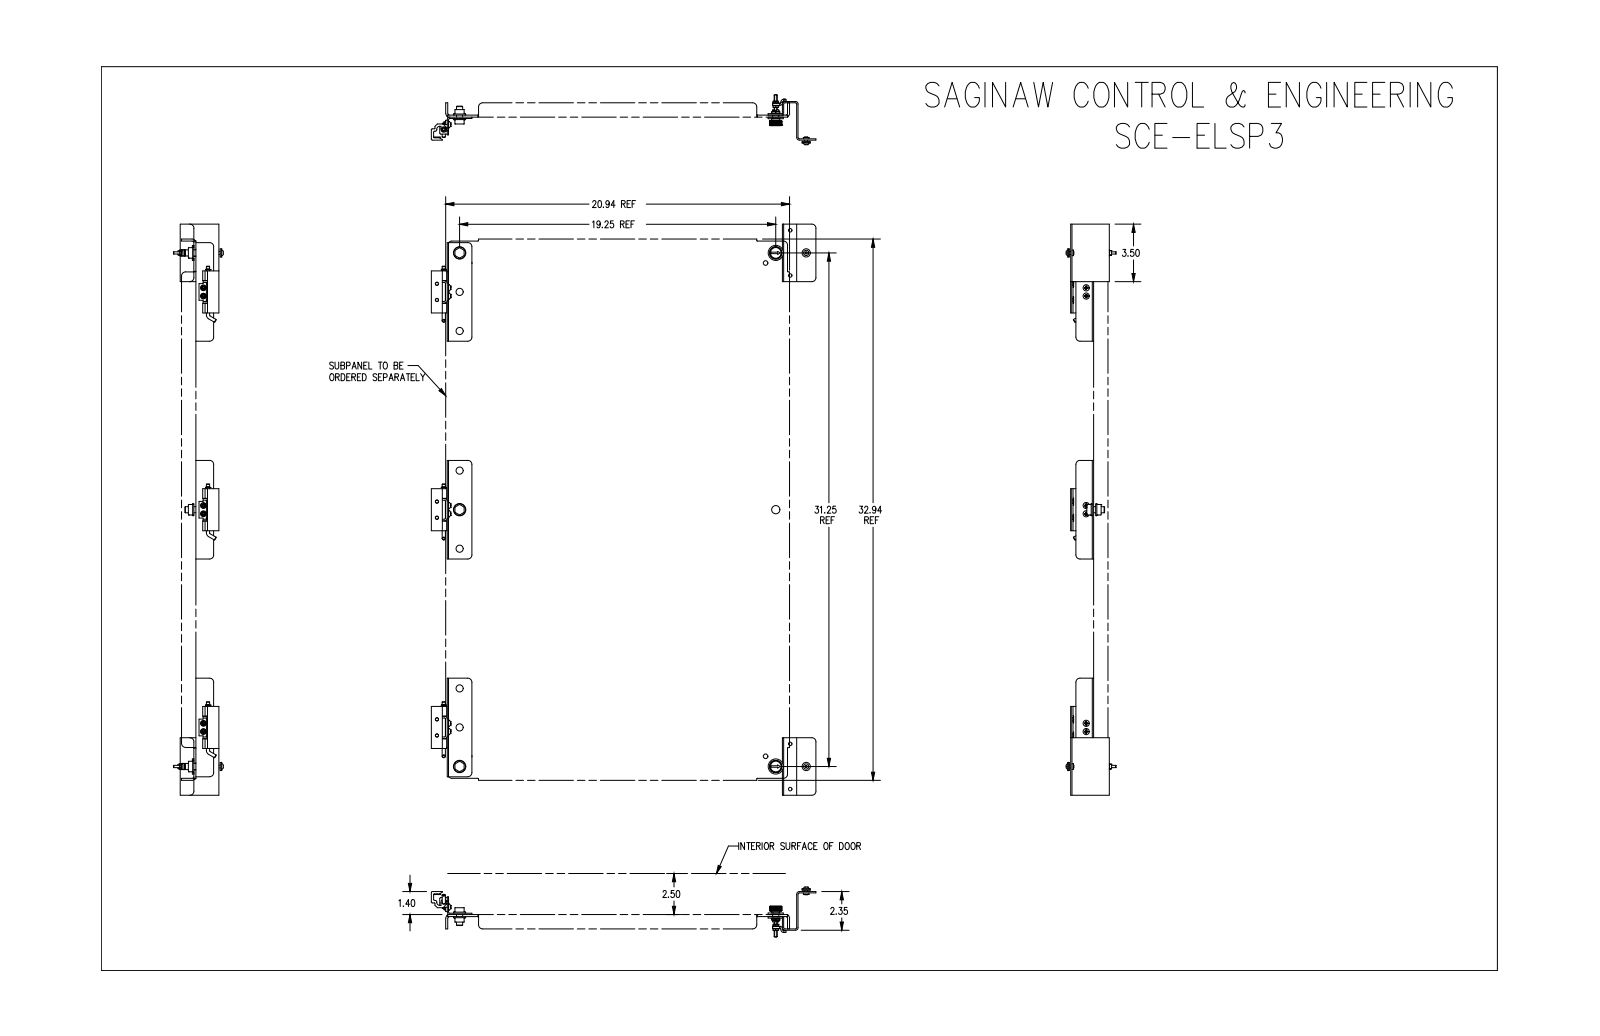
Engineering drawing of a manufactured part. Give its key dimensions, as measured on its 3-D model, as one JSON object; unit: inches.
{"part_name": "SCE-ELSP3", "step_written_by": "SolidWorks 2021 (AUTOMOTIVE_DESIGN)", "units": "inches", "bodies": {"solids": 74, "faces": 1943, "planar": 940, "cylindrical": 457, "other": 546}, "overall_size": [34.75, 23.418, 3.083], "volume_in3": 103.6, "surface_area_in2": 1767, "round_holes": [[0.19, 16], [0.218, 10], [0.437, 9], [0.25, 8], [0.2, 6], [0.5, 6], [0.281, 4], [0.367, 3], [0.125, 2], [0.204, 2], [0.212, 2], [0.249, 2]], "round_bosses_or_shafts": [[0.373, 9], [0.34, 8], [0.249, 6], [0.188, 6], [0.196, 4], [0.92, 2], [0.5, 2], [0.493, 2]], "partial_cylinders_radius": [[0.25, 28], [0.031, 26], [0.01, 25], [0.06, 7], [0.005, 6], [0.07, 6], [0.104, 6], [0.174, 6]], "face_to_face_distances": [0.125, 0.078, 0.125, 20.813, 21.278, 0.203, 32.813, 20.687, 0.094, 0.031], "hole_center_spacings": [13.25, 26.5, 0.875, 1.465, 18.641, 19.396, 24.793, 19.25]}
